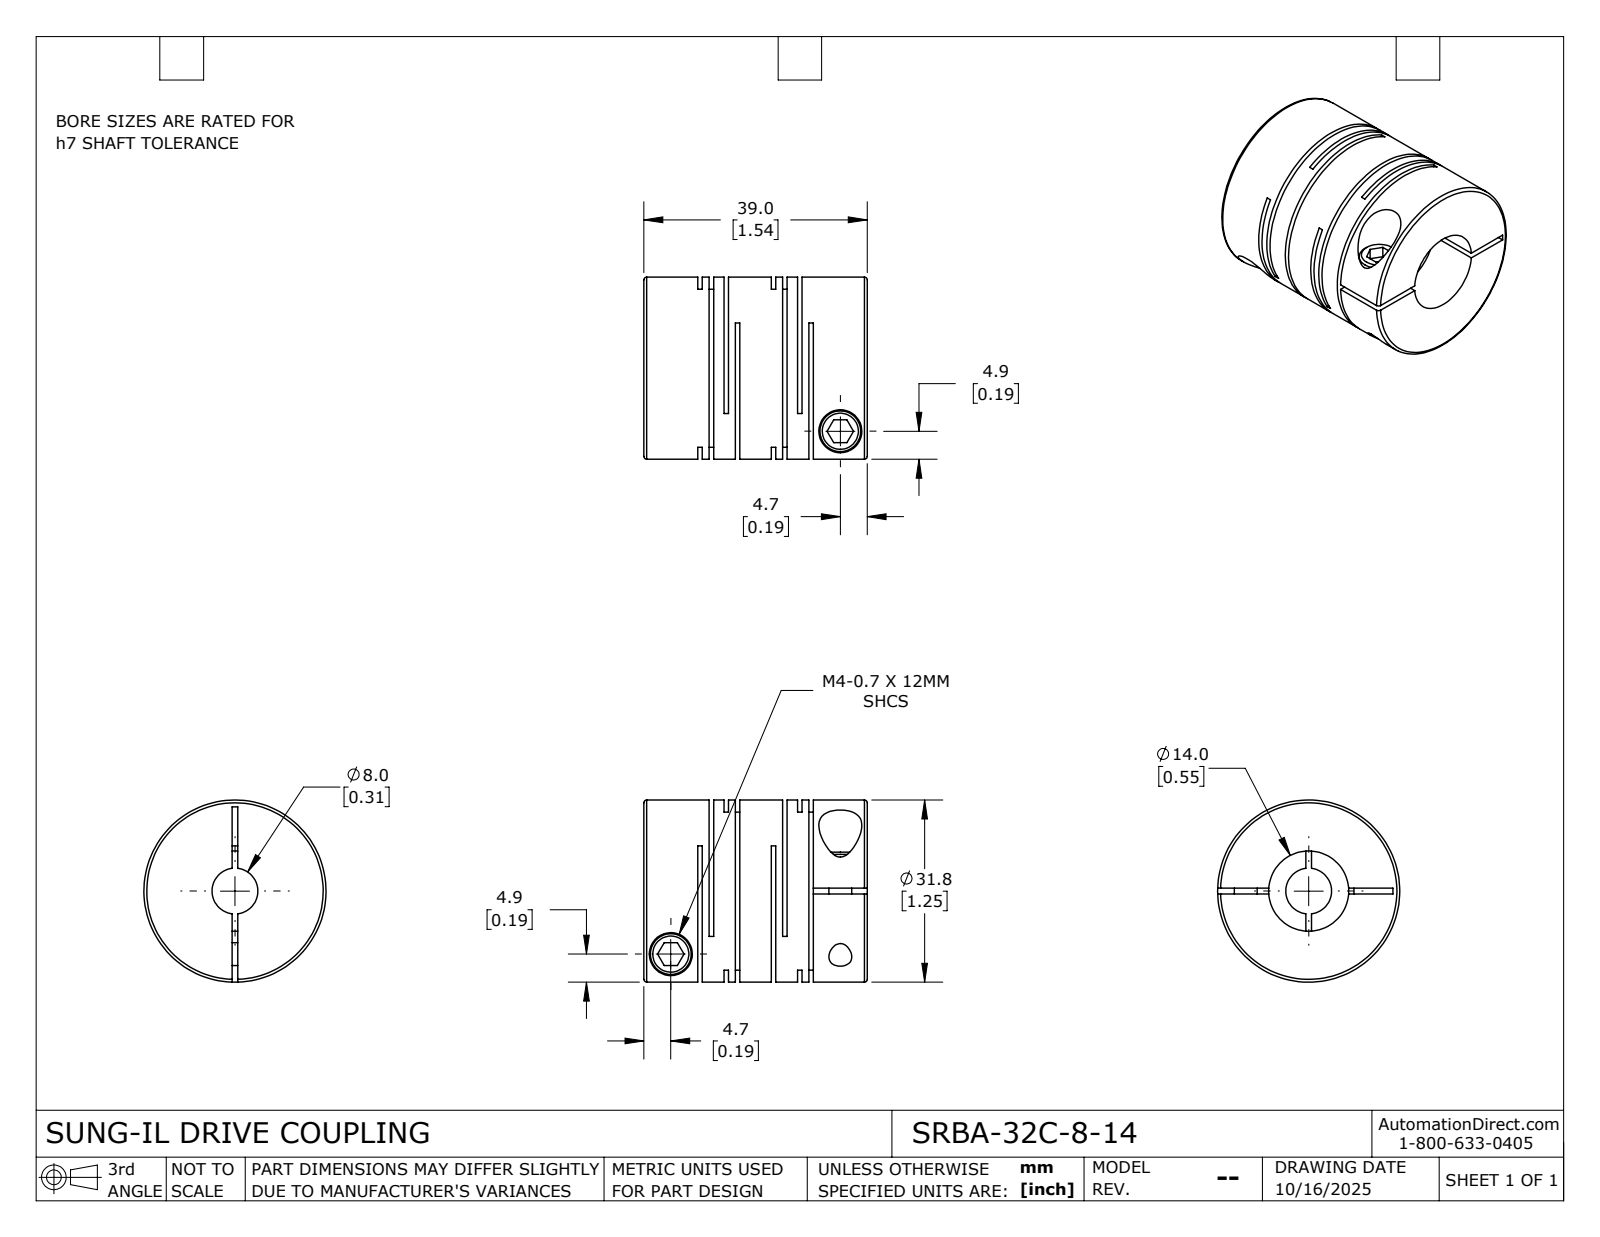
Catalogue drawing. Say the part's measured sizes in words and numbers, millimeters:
The part is named "SRBA-32C-8-14". Its 3-D file was written by "SolidWorks 2024 (CONFIG_CONTROL_DESIGN)". It is 1 solid with 115 faces: 60 planar, 42 cylindrical and 13 other. Overall it measures 39 by 31.8 by 31.8 millimeters. Its volume is 21 965 cubic millimeters and its surface area 15 254 square millimeters. Round holes: 2 of diameter 4, 2 of diameter 7.5, 1 of diameter 8, 1 of diameter 14. Round bosses or shafts: 2 of diameter 7.1, 1 of diameter 31.8. The main face-to-face distances are 0.8, 12.84, 1.98, 4.58, 12.04, 1.18, 10.86, 3.78, 8.26, 2.6.
